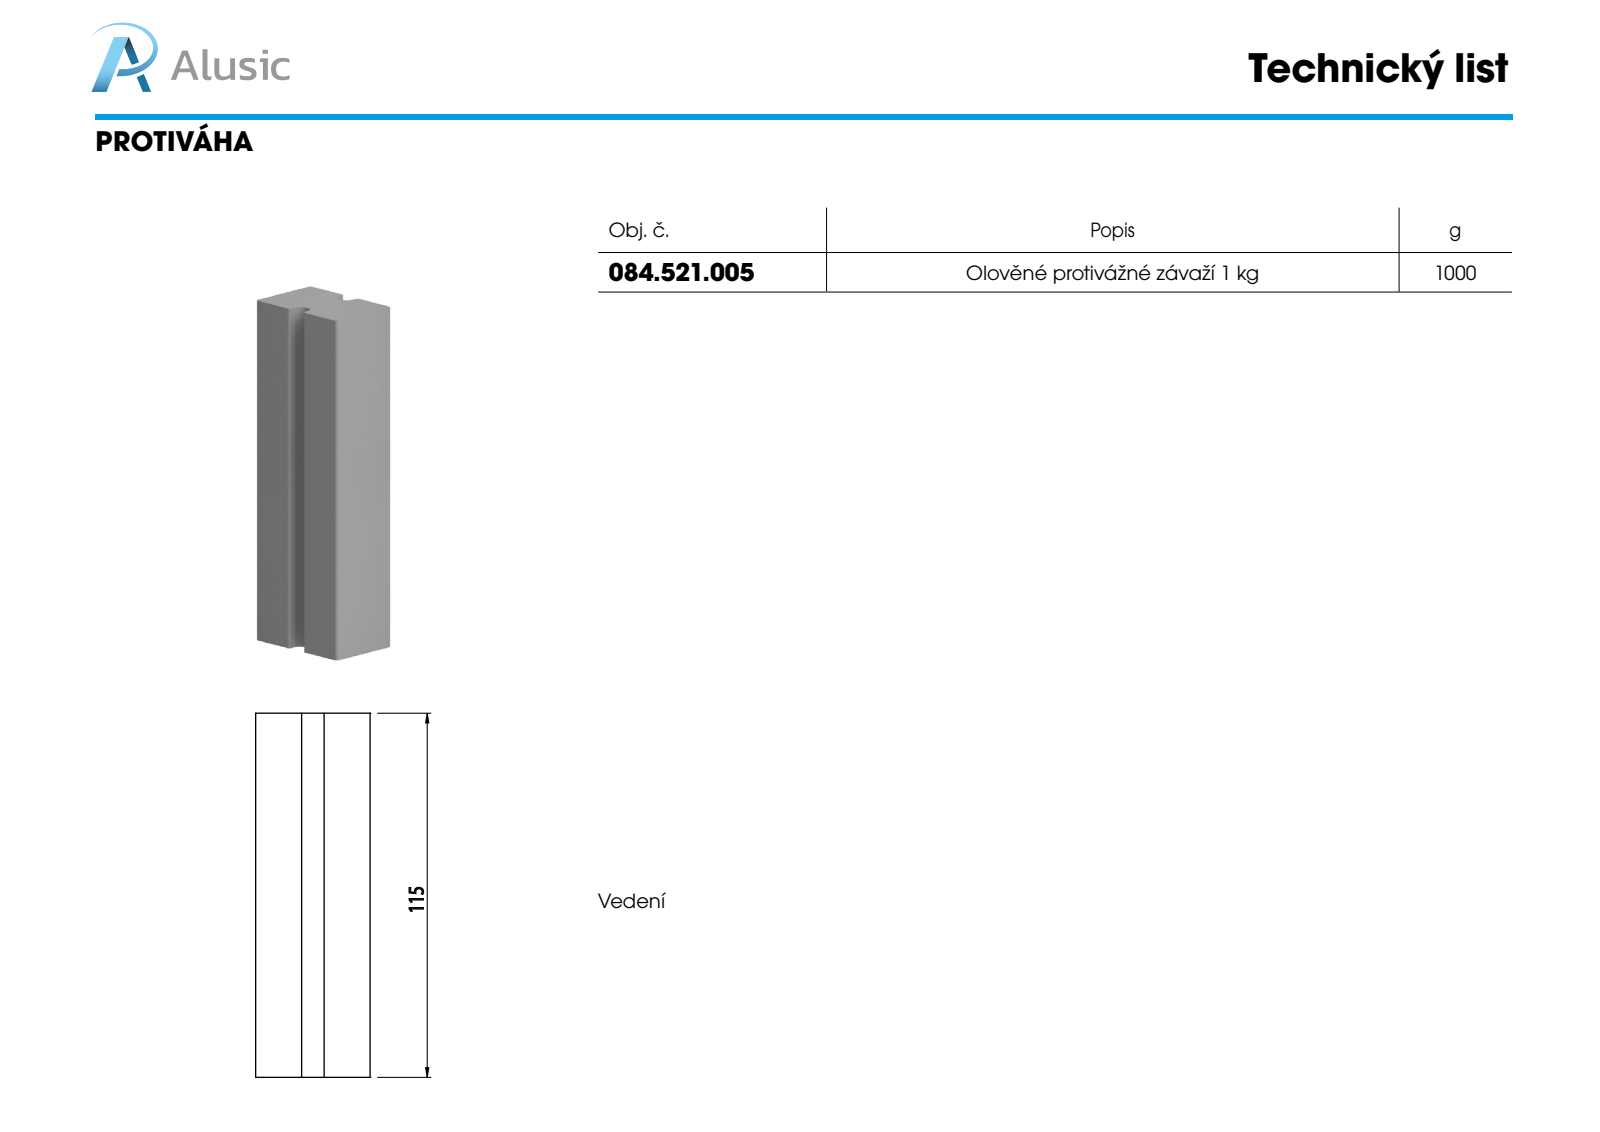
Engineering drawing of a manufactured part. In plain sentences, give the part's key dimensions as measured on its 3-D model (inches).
The part is named "084.521.005". Its 3-D file was written by "SolidWorks 2011 (CONFIG_CONTROL_DESIGN)". It is 1 solid with 23 faces: 12 planar, 11 cylindrical and 0 other. Overall it measures 4.469 by 1.457 by 0.984 inches. Its volume is 6.033 cubic inches and its surface area 26.52 square inches. Partial cylindrical surfaces (rounded edges, fillets, slot ends): 8 of radius 0.039, 2 of radius 0.118. The main face-to-face distances are 0.984, 1.457, 4.469, 0.61, 0.846, 0.236.
